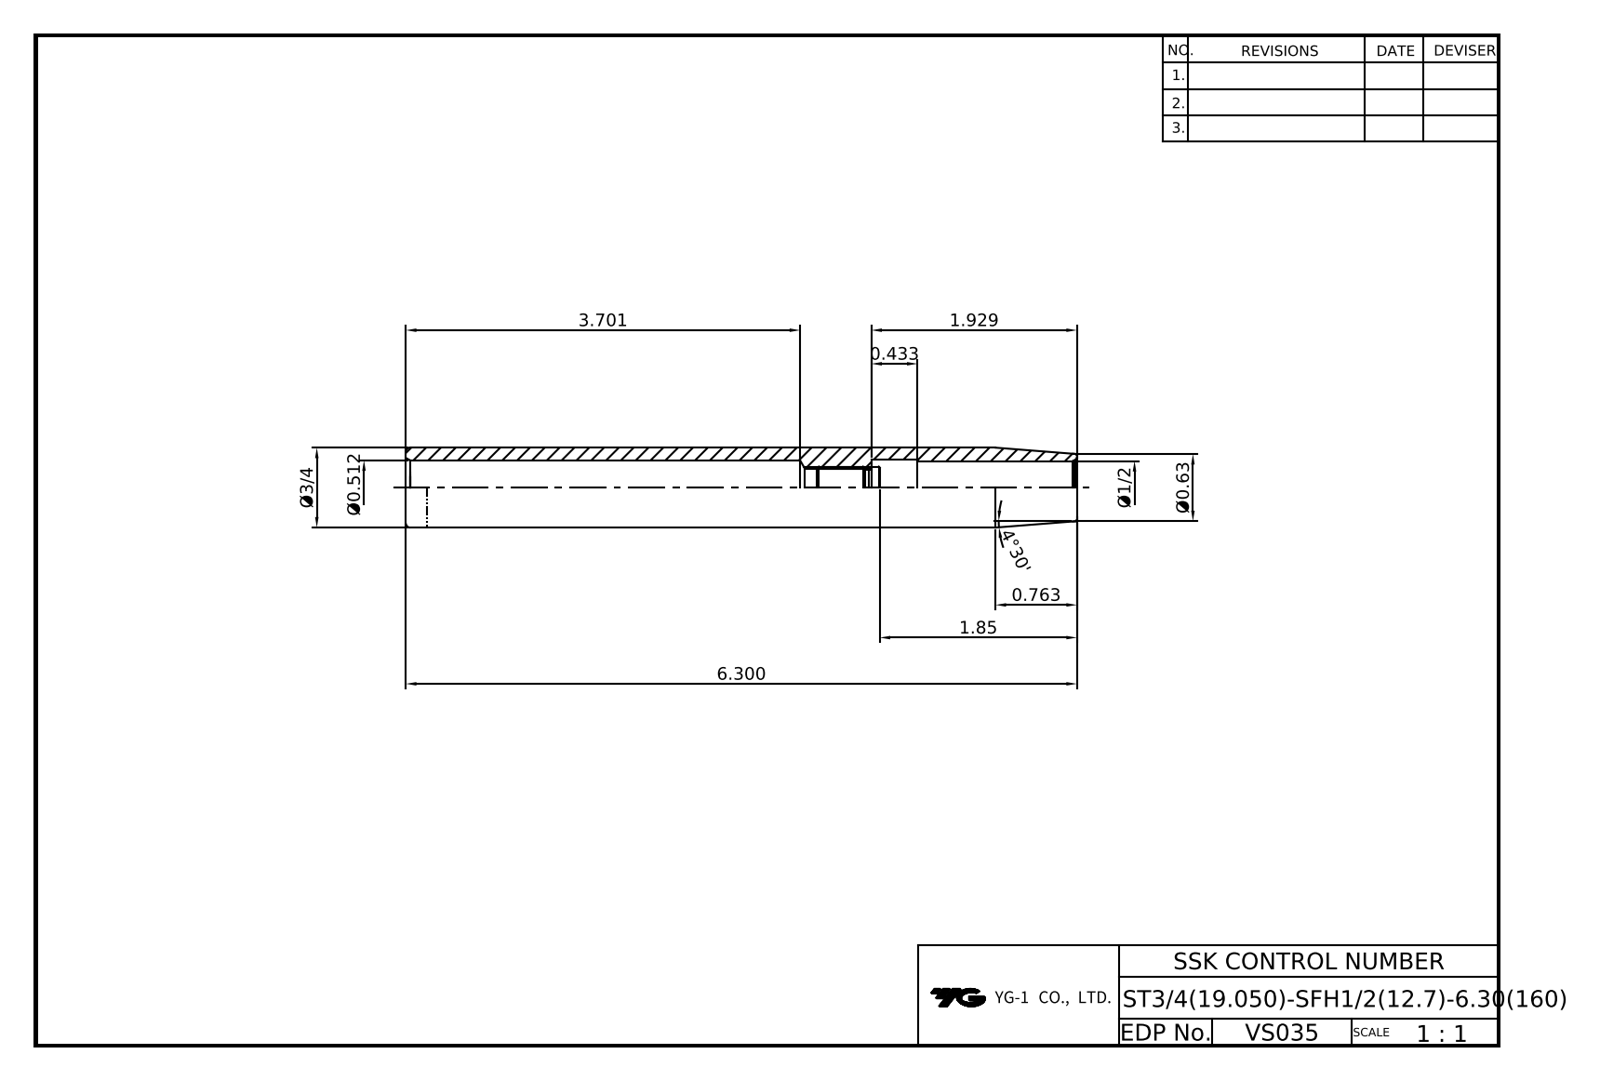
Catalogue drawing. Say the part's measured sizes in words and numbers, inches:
The part is named "ST19.05-SFH12.7-160(20240111)". Its 3-D file was written by "Autodesk Inventor 2024 (AUTOMOTIVE_DESIGN)". It is 1 solid with 16 faces: 4 planar, 5 cylindrical and 7 other. Overall it measures 6.299 by 0.75 by 0.75 inches. Its volume is 1.509 cubic inches and its surface area 24.98 square inches. Round holes: 1 of diameter 0.351, 1 of diameter 0.5, 1 of diameter 0.512, 1 of diameter 0.539. Round bosses or shafts: 1 of diameter 0.75. The main face-to-face distances are 4.37, 4.803, 0.433, 6.299, 1.929, 1.496.
